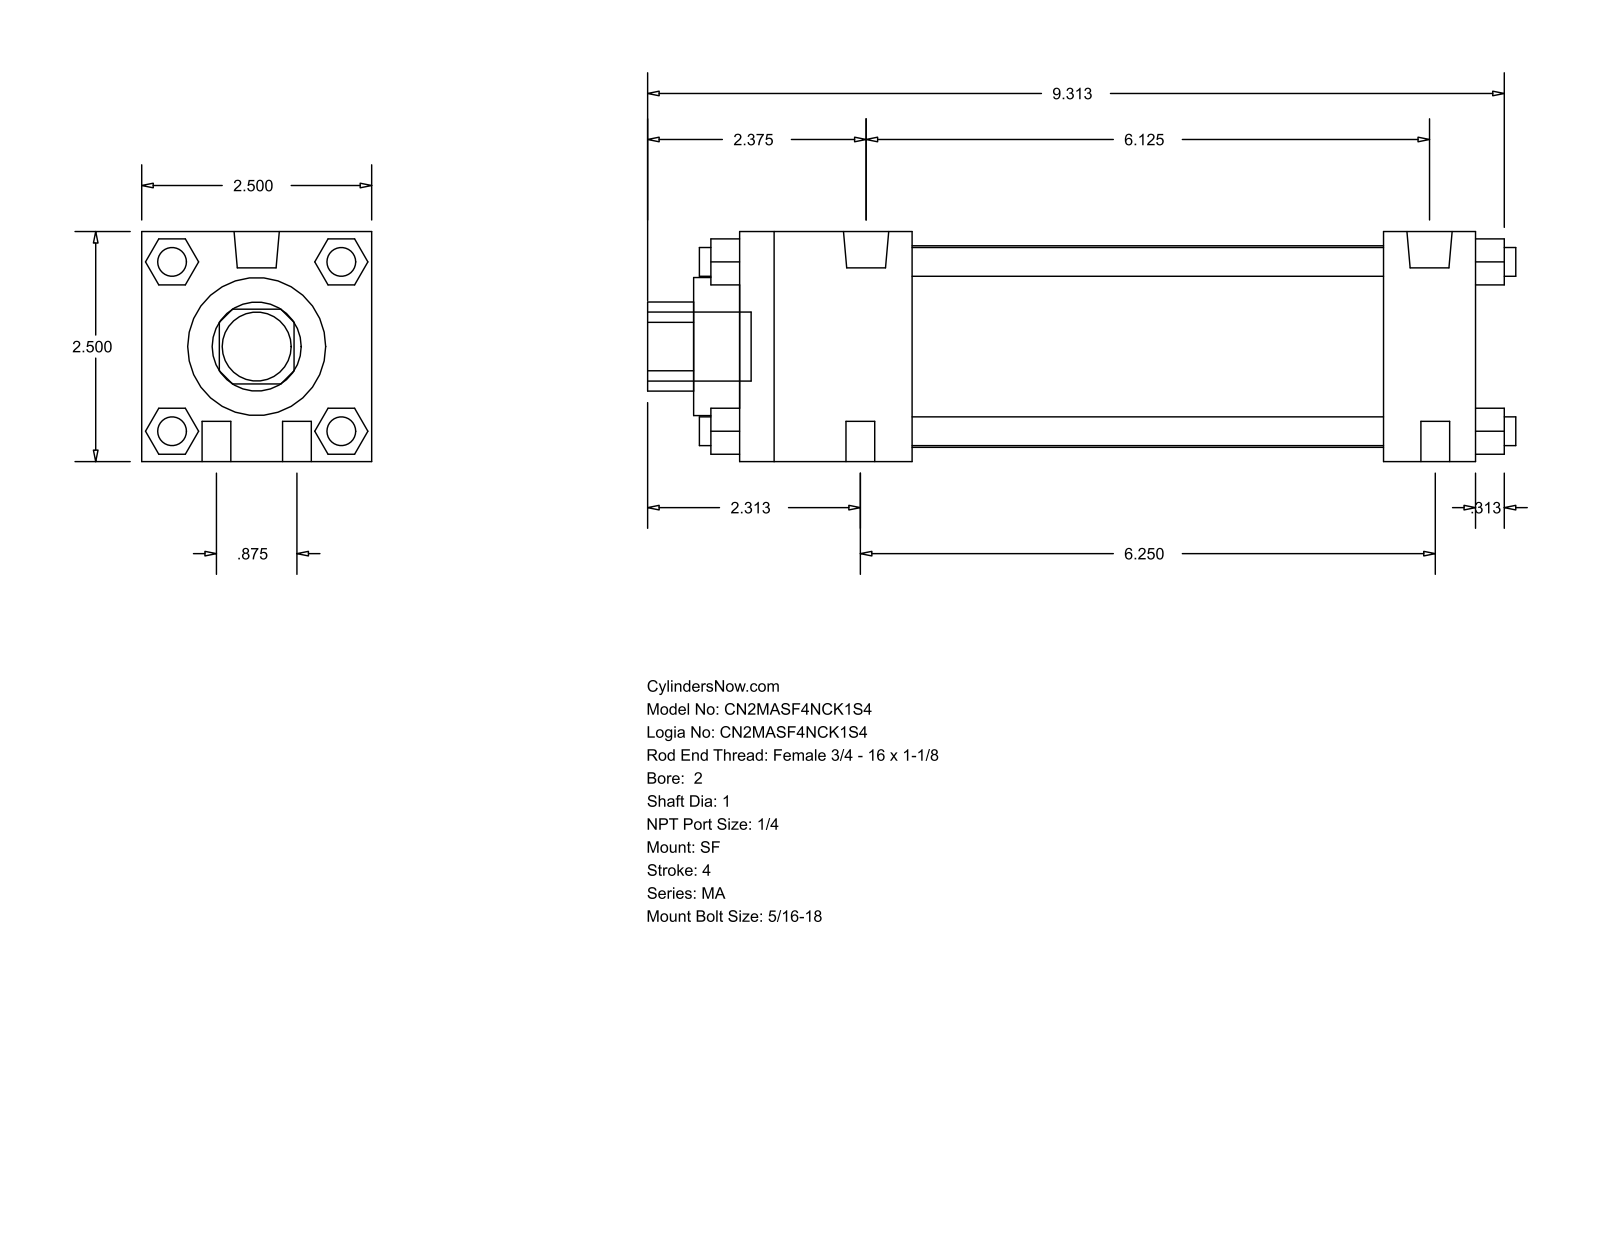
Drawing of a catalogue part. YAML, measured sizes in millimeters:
part_name: "MA_SF__0200_1"
step_written_by: "GSSL Pune (CONFIG_CONTROL_DESIGN)"
units: millimeters
bodies: {solids: 0, faces: 124, planar: 94, cylindrical: 30, other: 0}
overall_size: [239.71, 63.5, 63.5]
round_holes:
  - {diameter: 25.4, count: 1}
  - {diameter: 38.1, count: 1}
  - {diameter: 55.63, count: 1}
round_bosses_or_shafts:
  - {diameter: 7.94, count: 10}
  - {diameter: 12.49, count: 2}
  - {diameter: 19.05, count: 1}
partial_cylinders:
  - {radius: 12.29, count: 1}
face_to_face_distances: [63.5, 203.2, 12.7, 25.4, 177.8, 47.63, 130.17, 155.57, 23.37, 40.47]
